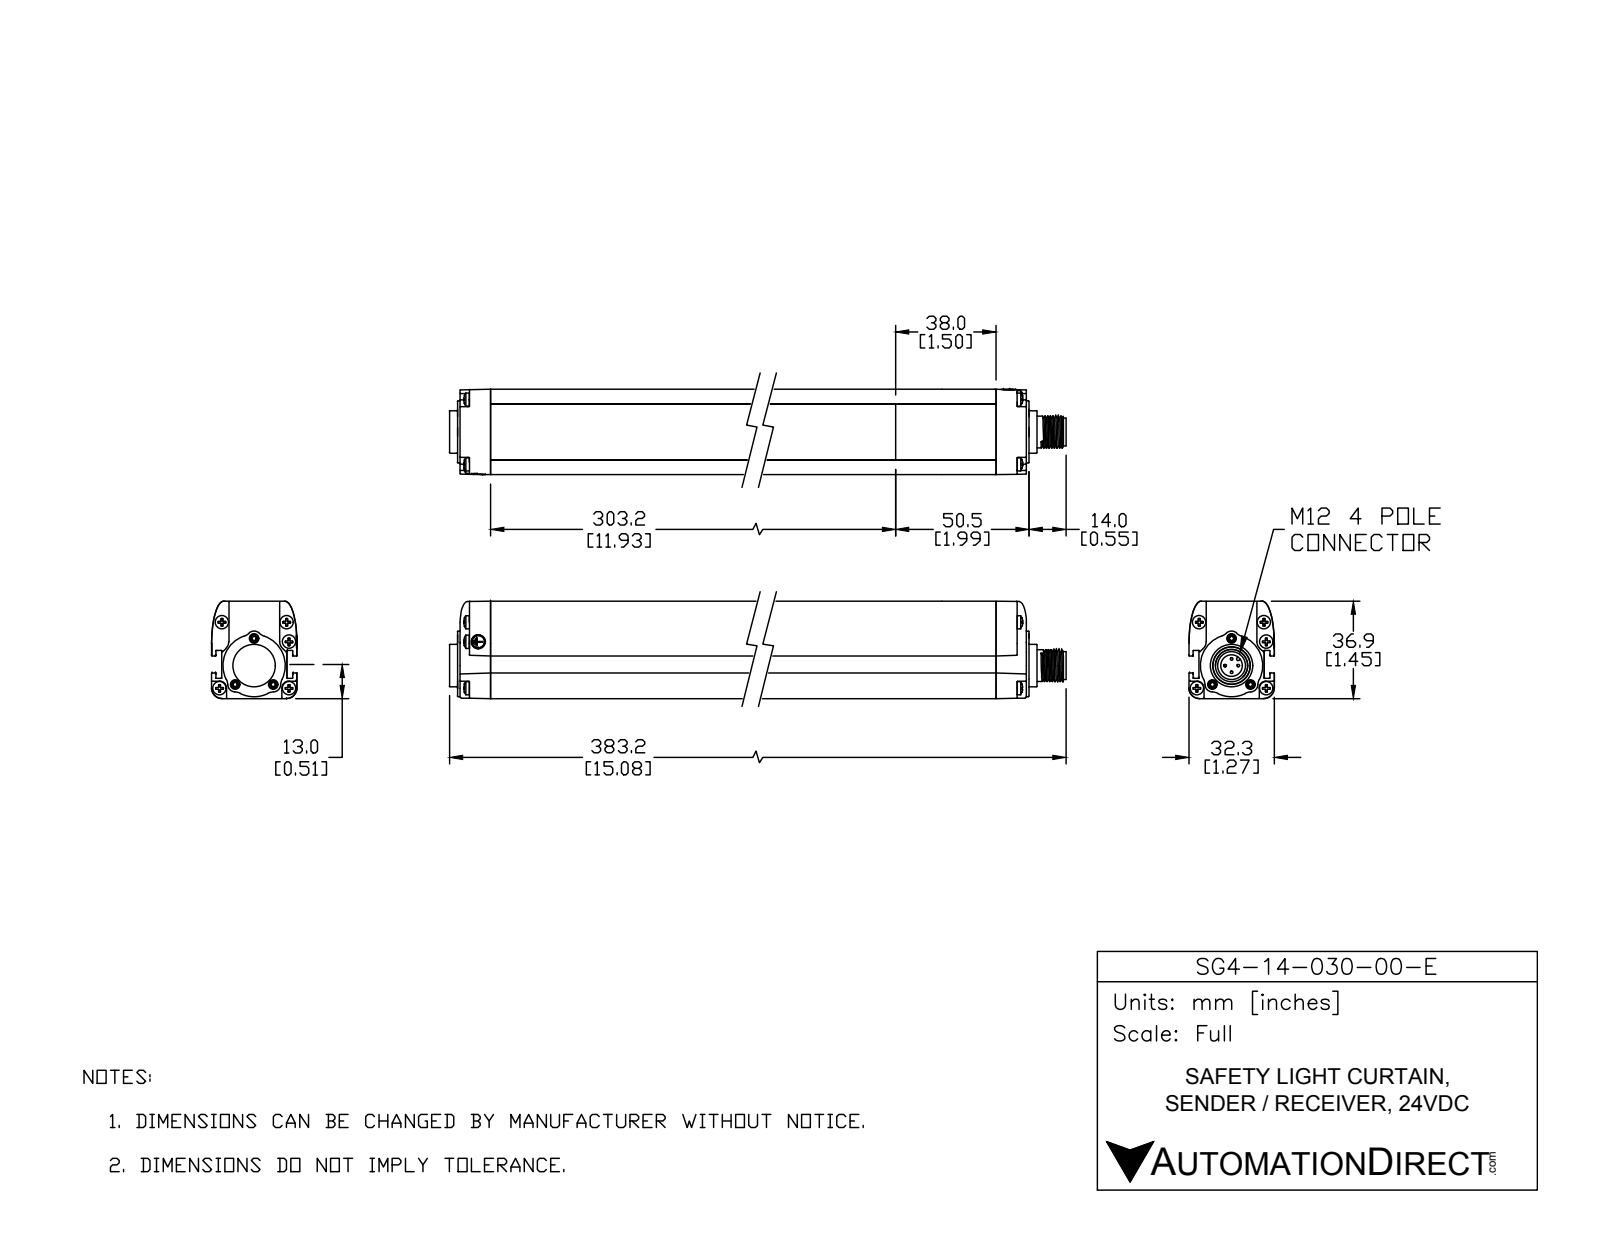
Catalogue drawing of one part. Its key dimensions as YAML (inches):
part_name: "SG4-14-030-OO-E"
step_written_by: "SolidWorks 2017 (AUTOMOTIVE_DESIGN)"
units: inches
bodies: {solids: 29, faces: 1674, planar: 410, cylindrical: 591, other: 673}
overall_size: [15.075, 2.48, 2.055]
volume: 23.89
surface_area: 165.8
round_holes:
  - {diameter: 0.106, count: 6}
  - {diameter: 0.209, count: 6}
  - {diameter: 0.081, count: 4}
  - {diameter: 0.165, count: 4}
  - {diameter: 0.26, count: 4}
  - {diameter: 0.059, count: 3}
  - {diameter: 0.142, count: 3}
  - {diameter: 0.323, count: 1}
  - {diameter: 0.376, count: 1}
  - {diameter: 0.433, count: 1}
  - {diameter: 0.563, count: 1}
round_bosses_or_shafts:
  - {diameter: 0.197, count: 10}
  - {diameter: 0.394, count: 4}
  - {diameter: 0.039, count: 4}
  - {diameter: 0.185, count: 2}
  - {diameter: 0.63, count: 1}
  - {diameter: 0.55, count: 1}
  - {diameter: 0.472, count: 1}
  - {diameter: 0.413, count: 1}
partial_cylinders:
  - {radius: 0.008, count: 148}
  - {radius: 0.004, count: 120}
  - {radius: 0.006, count: 18}
  - {radius: 0.106, count: 18}
  - {radius: 0.118, count: 8}
  - {radius: 0.197, count: 7}
  - {radius: 0.11, count: 3}
  - {radius: 0.016, count: 2}
face_to_face_distances: [0.079, 1.272, 0.15, 1.429, 1.122, 1.35, 0.118, 0.157, 0.972, 0.333]
hole_center_spacings: [0.569, 11.847, 0.402, 0.24, 0.293, 0.52, 0.541, 0.619]
